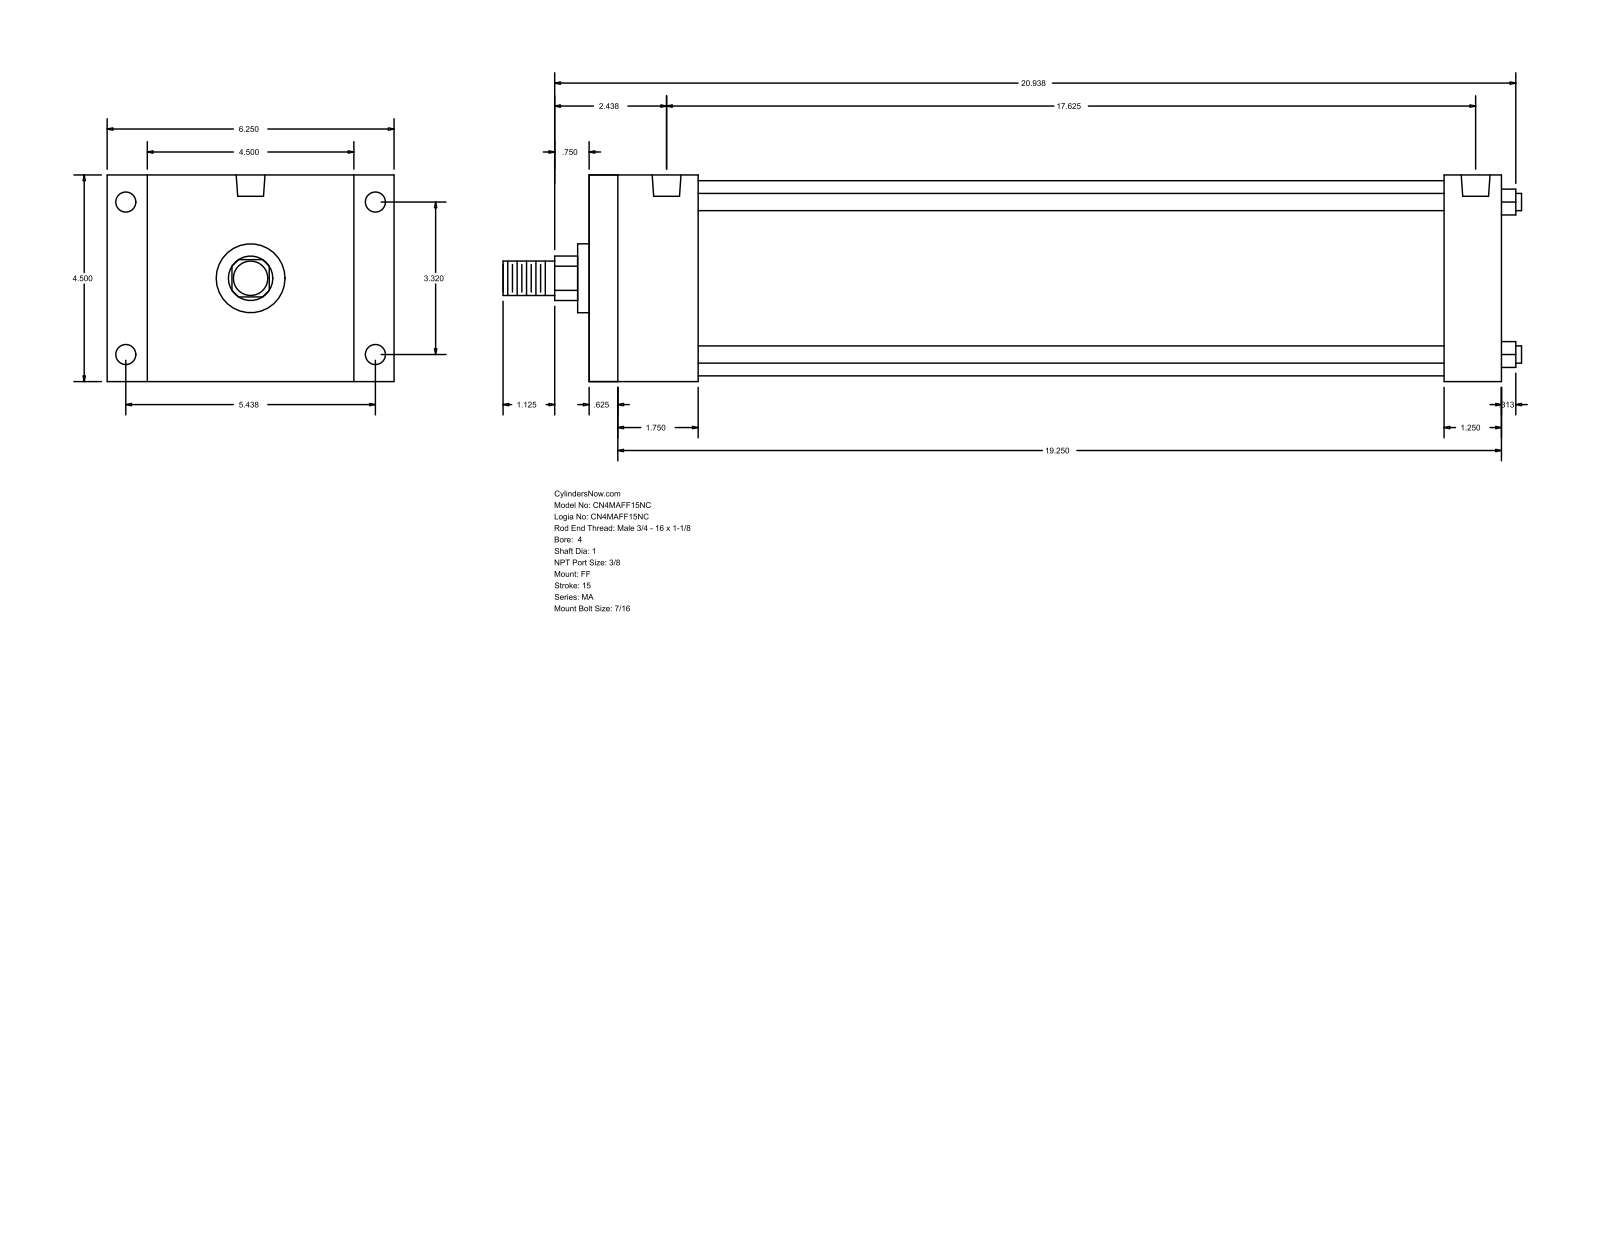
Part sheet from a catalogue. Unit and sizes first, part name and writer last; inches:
Units: inches
Overall size (bounding box): 22.187 × 6.25 × 4.5
Round holes (diameter × count): ⌀0.437 ×8, ⌀0.627 ×2
Round bosses / shafts (diameter × count): ⌀0.375 ×4, ⌀4.25 ×1, ⌀1.5 ×1, ⌀1 ×1, ⌀0.75 ×1
Partial cylindrical surfaces — rounded edges, fillets, slot ends (radius × count): R0.484 ×1
Main face-to-face distances: 4.5, 19.875, 0.625, 19.25, 0.875, 5.375, 18.625, 18, 1.25, 2.375
Hole centre spacings: 3.32, 5.438, 6.371, 17.25, 0.187, 0.188, 17.437, 17.438
Bodies: 0 solids, 92 faces (64 planar, 28 cylindrical, 0 other)
Part name (STEP PRODUCT): MA_FF__0400_1
STEP written by: GSSL Pune (CONFIG_CONTROL_DESIGN)
